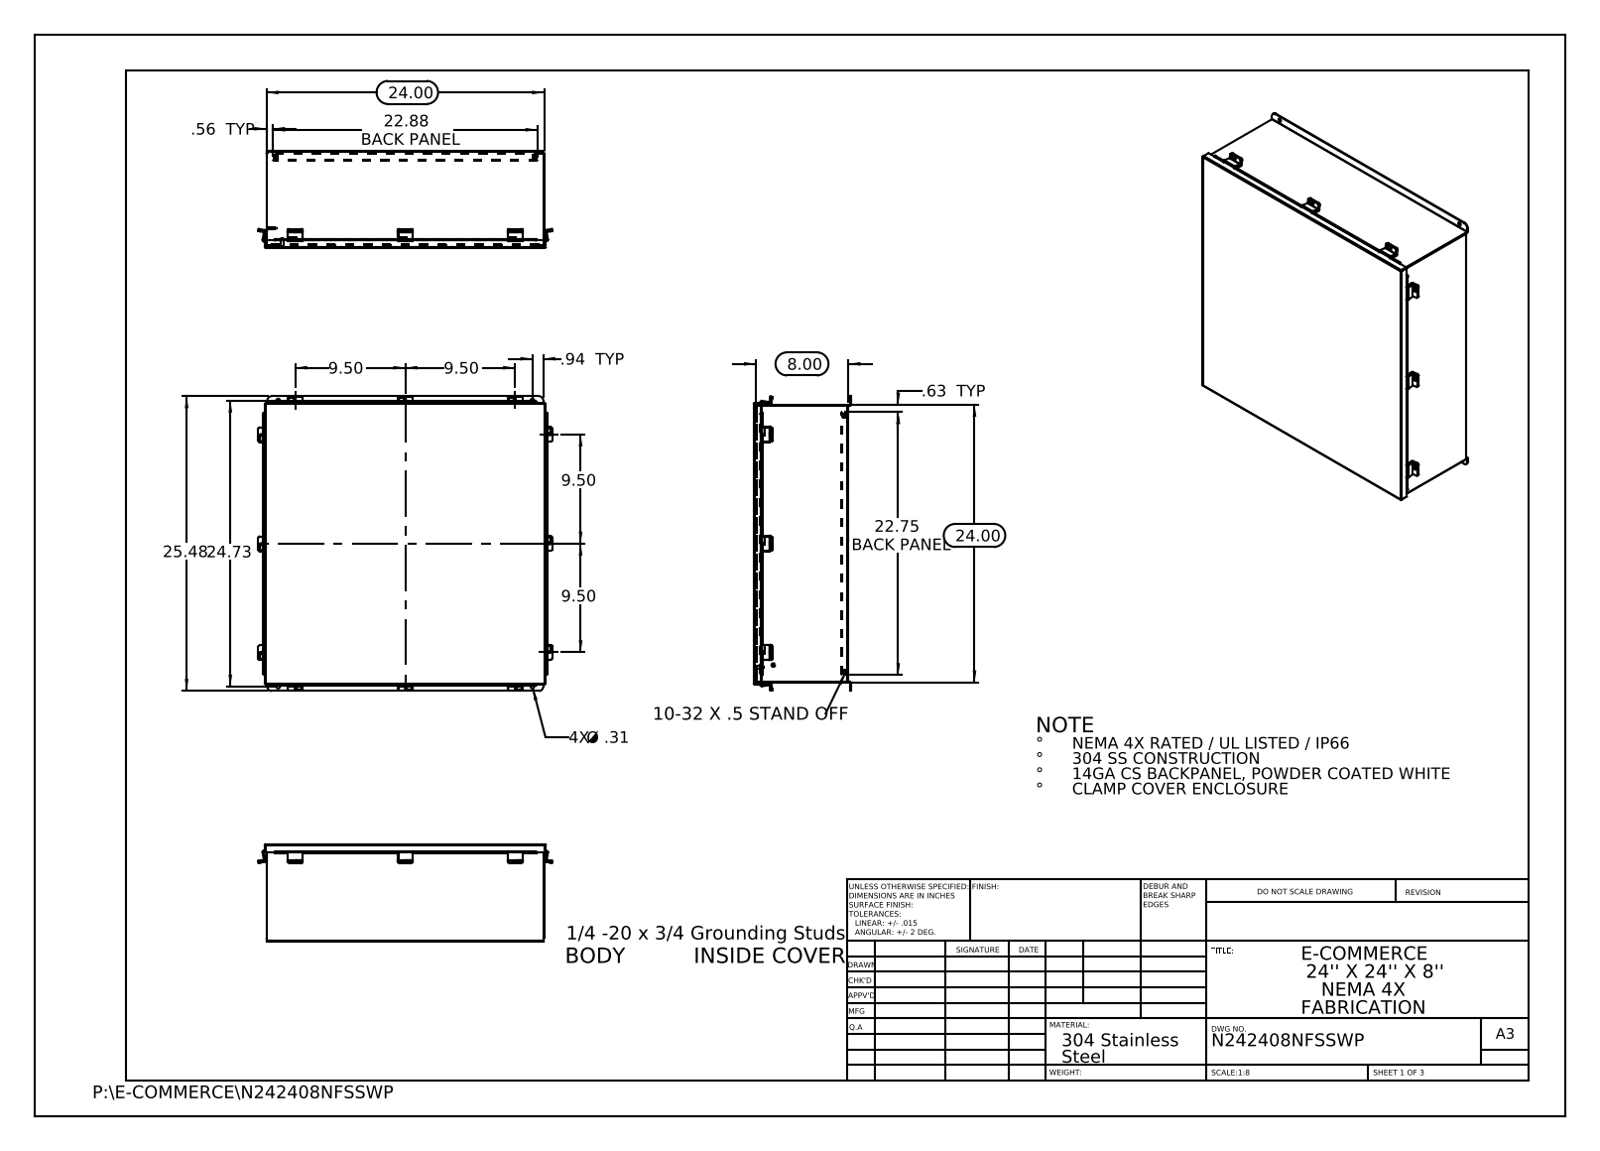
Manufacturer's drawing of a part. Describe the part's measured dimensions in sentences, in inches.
The part is named "N242408NFSSWP JIC_Standoff; N242408NFSSWP JIC Bottom; N242408NFSSWP JIC Cover Clamp; N242408NFSSWP HW-CD-S-25020-034 (+6 more)". Its 3-D file was written by "SolidWorks 2013 (CONFIG_CONTROL_DESIGN)". It is 35 solids with 824 faces: 548 planar, 256 cylindrical and 20 other. Overall it measures 25.476 by 25.407 by 8.39 inches. Its volume is 196.3 cubic inches and its surface area 5 292 square inches. Round holes: 16 of diameter 0.25, 4 of diameter 0.187, 4 of diameter 0.312. Round bosses or shafts: 4 of diameter 0.313, 2 of diameter 0.315, 2 of diameter 0.236. Partial cylindrical surfaces (rounded edges, fillets, slot ends): 42 of radius 0.125, 24 of radius 0.133, 16 of radius 0.009, 12 of radius 0.013, 12 of radius 0.088, 8 of radius 0.083, 8 of radius 0.1, 4 of radius 0.084. The main face-to-face distances are 0.075, 8.128, 23.925, 8.053, 8.203, 7.628, 0.575, 0.5, 7.553, 0.649. The hole center spacings are 1.315, 9.425, 9.5, 22.213, 23.427, 32.257, 18.85, 19.
